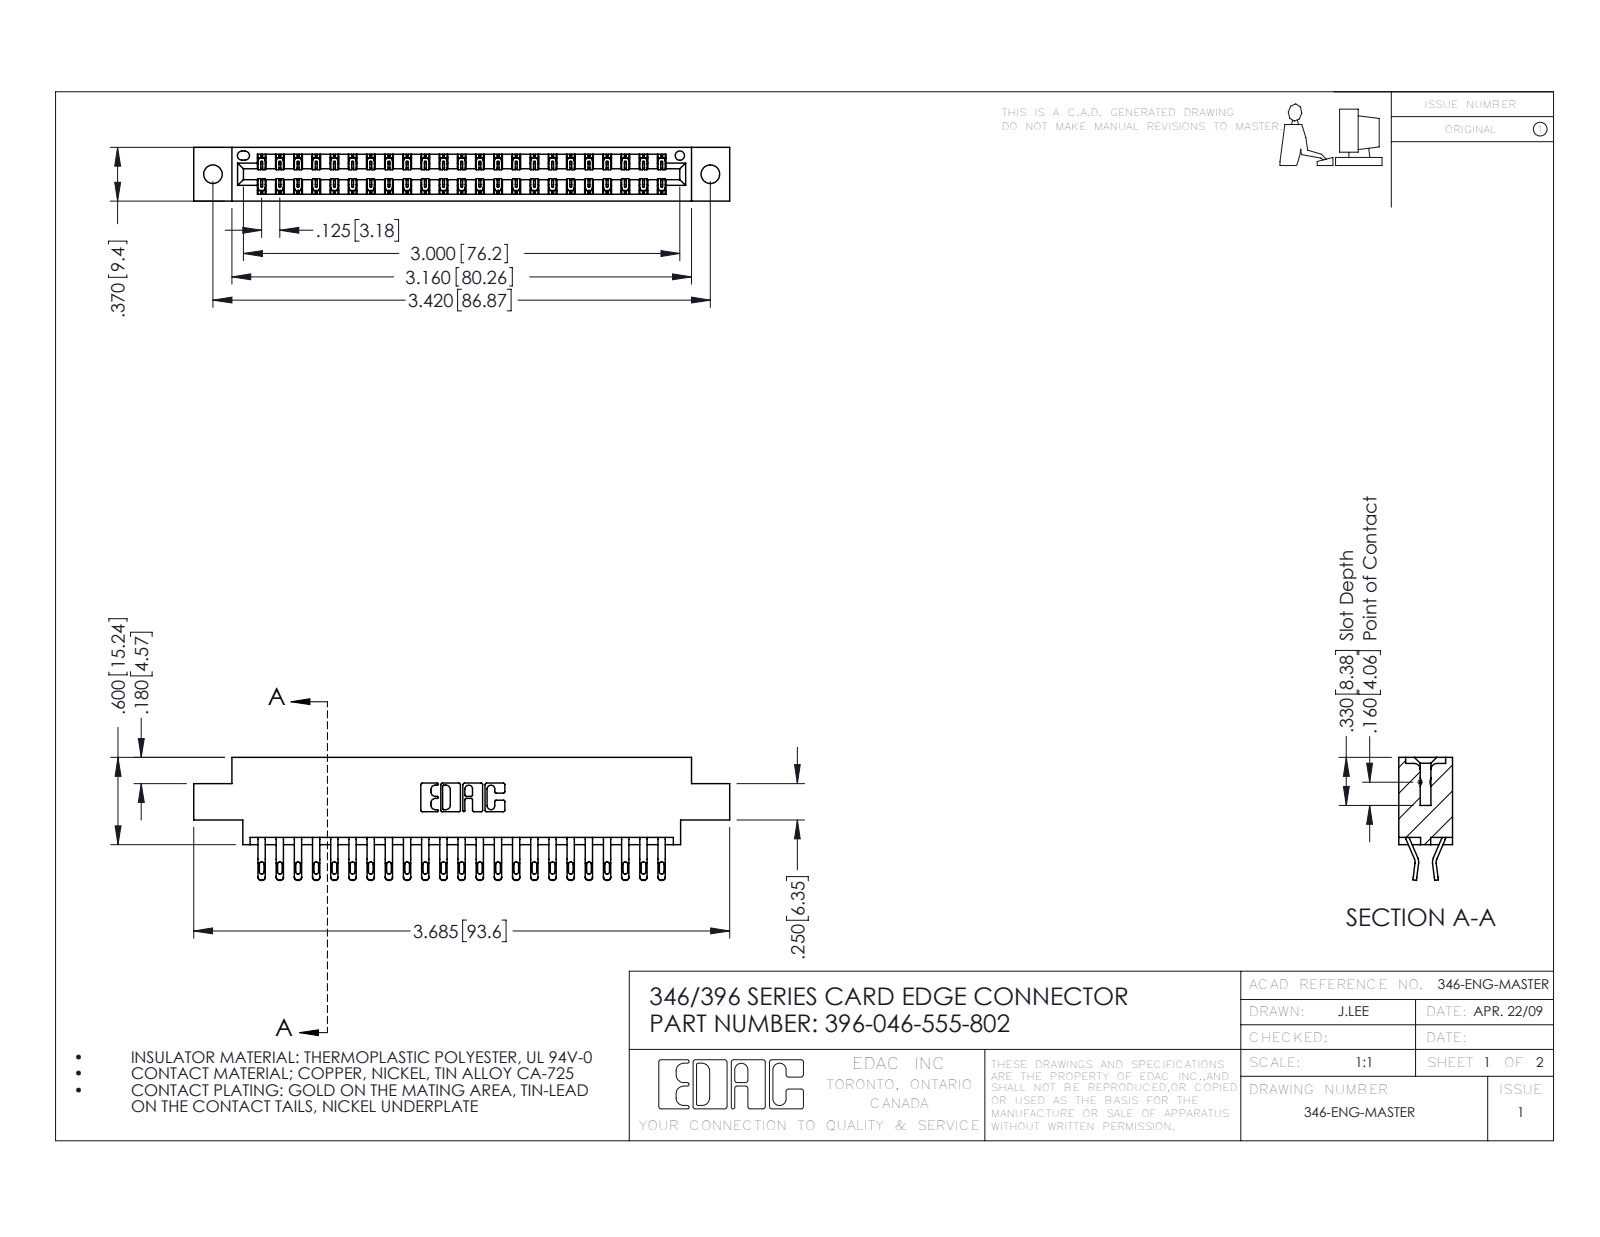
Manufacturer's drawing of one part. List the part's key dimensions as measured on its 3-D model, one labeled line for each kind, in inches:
Part name (STEP PRODUCT): 396-046-555-802; 346 Part_0.170 Offset - 0.128 Dia; 345-292-001_555 Tail
STEP written by: SolidWorks 2016 (CONFIG_CONTROL_DESIGN)
Units: inches
Bodies: 47 solids, 2794 faces (1598 planar, 1196 cylindrical, 0 other)
Overall size (bounding box): 3.685 × 0.845 × 0.37
Volume: 0.544 in³ · Surface area: 19.14 in²
Round holes (diameter × count): ⌀0.128 ×2, ⌀0.064 ×1
Partial cylindrical surfaces — rounded edges, fillets, slot ends (radius × count): R0.016 ×92, R0.02 ×92, R0.006 ×69, R0.01 ×22, R0.007 ×6, R0.031 ×6, R0.026 ×3, R0.01 ×2
Main face-to-face distances: 0.048, 0.322, 0.37, 0.25, 0.025, 0.072, 0.298, 0.275, 0.148, 0.222
Hole centre spacings: 0.246, 3.212, 3.42
